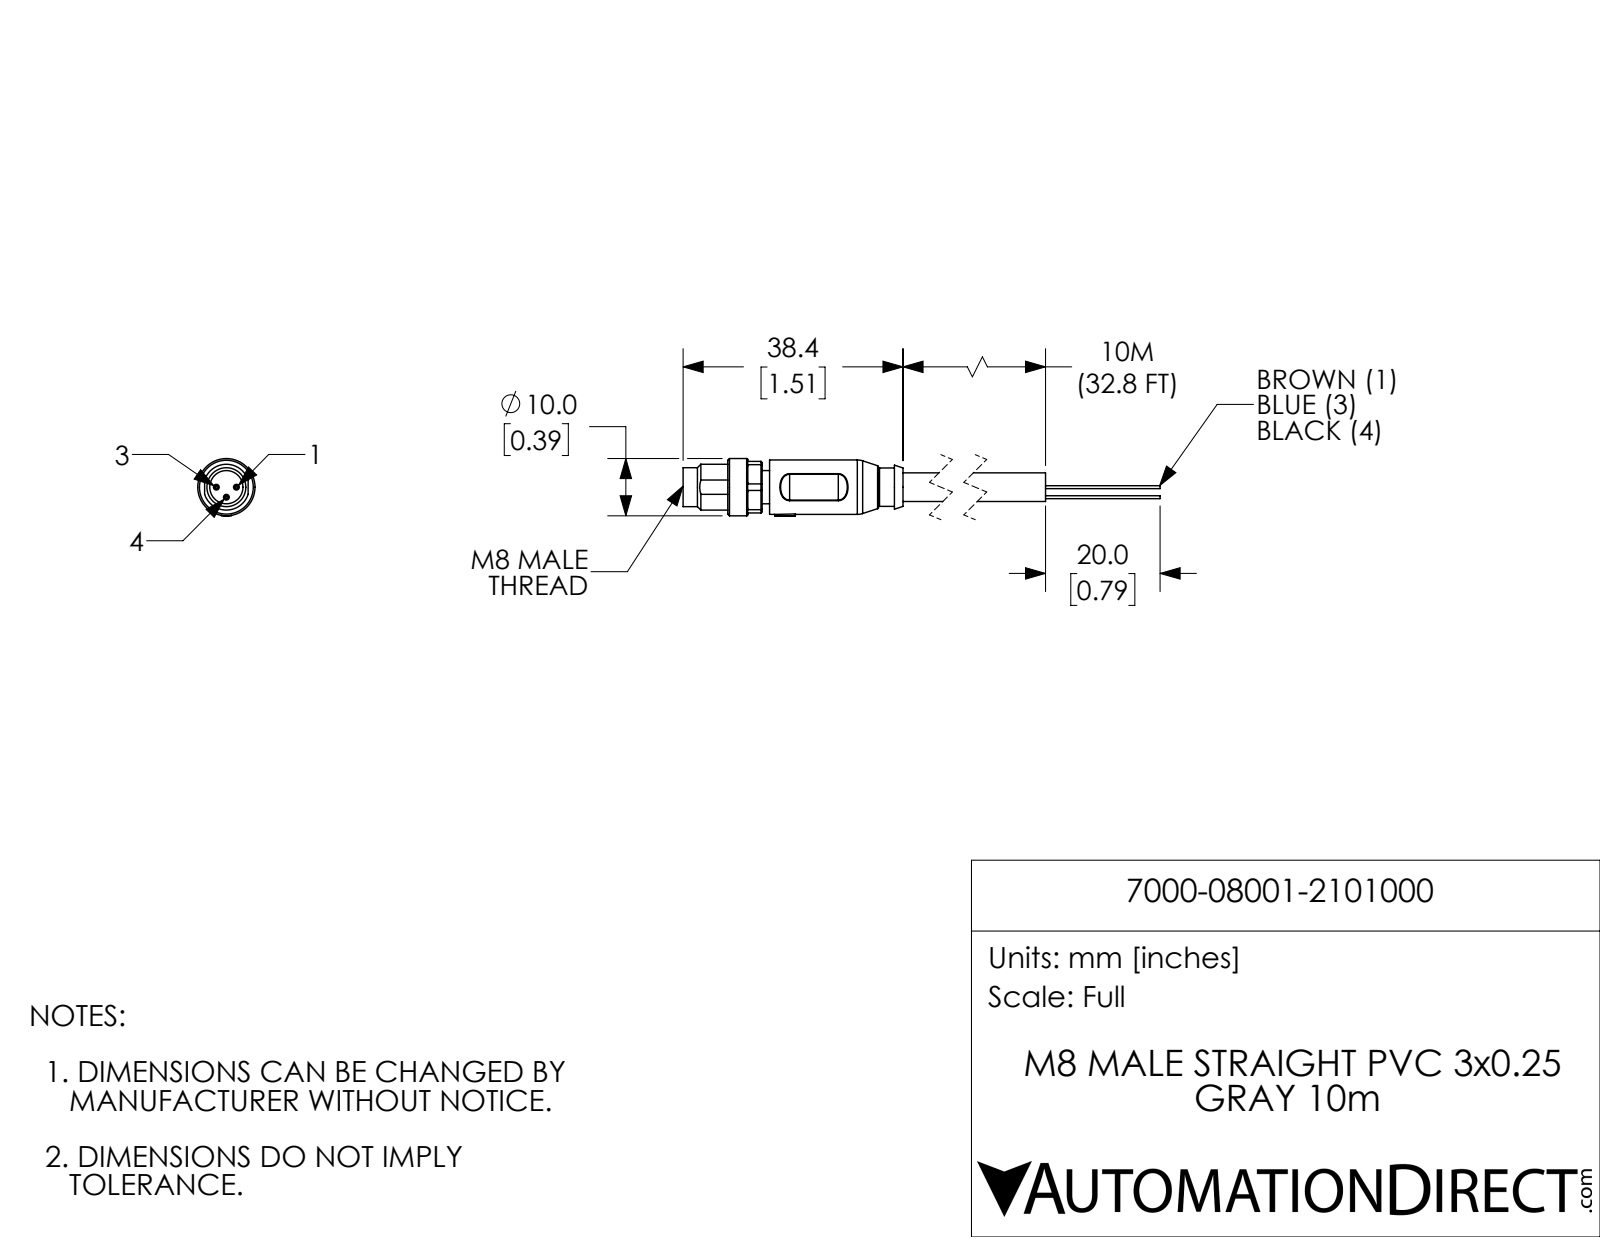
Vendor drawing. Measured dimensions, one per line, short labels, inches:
name: 7000-08001-2101000
written by: SolidWorks 2017 (AUTOMOTIVE_DESIGN)
unit: in
bodies: 4 solids, 119 faces (41 planar, 44 cylindrical, 34 other)
size: 3.087 × 0.396 × 0.394
volume: 0.155 in³; area: 2.792 in²
holes: 1× ⌀0.228
bosses: 3× ⌀0.039, 3× ⌀0.02, 1× ⌀0.394, 1× ⌀0.374, 1× ⌀0.315, 1× ⌀0.268, 1× ⌀0.264, 1× ⌀0.197
rounds: 4× R0.008, 4× R0.098, 1× R0.193, 1× R0.199
face distances: 0.327, 0.051, 0.354, 0.014, 0.313, 0.346, 0.398, 2.102, 1.756, 1.705
